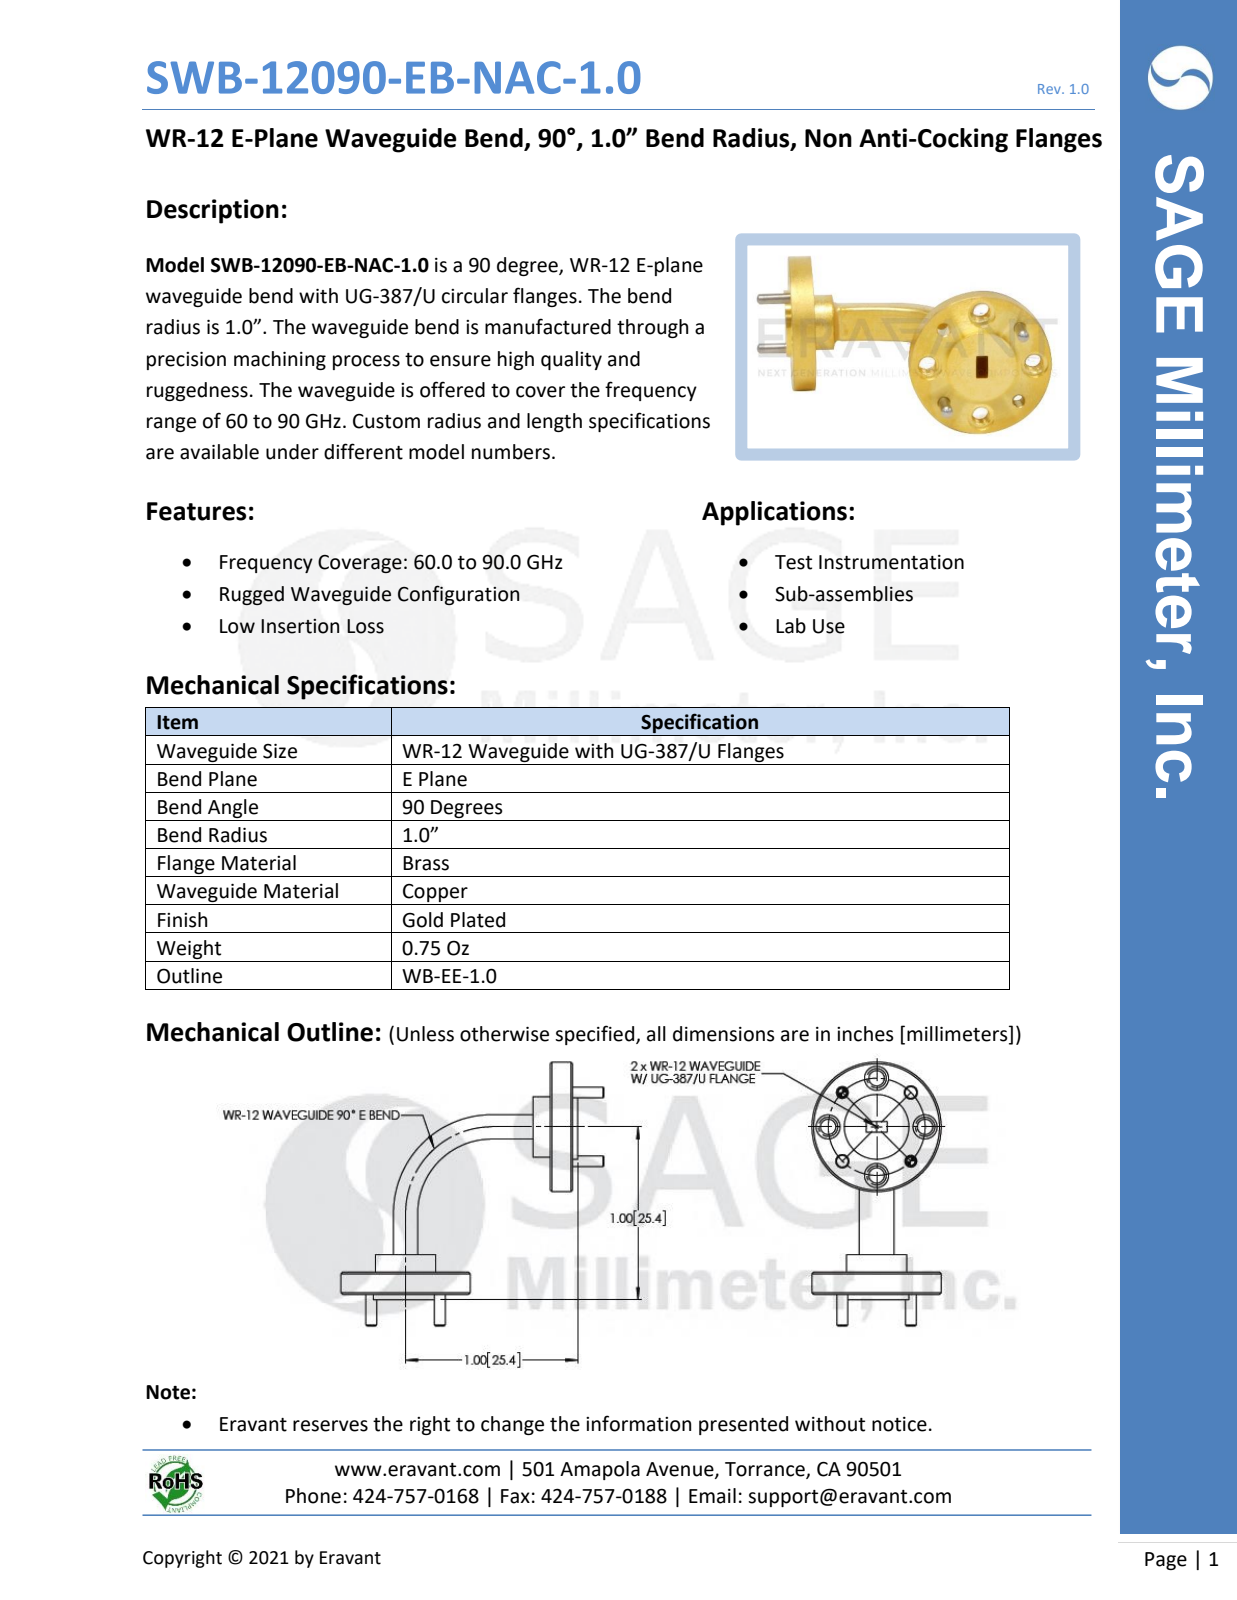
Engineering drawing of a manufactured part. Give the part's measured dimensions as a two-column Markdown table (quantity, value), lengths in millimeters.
| quantity | value |
| --- | --- |
| part name | SWB-12090-EB-1.0 |
| STEP written by | SolidWorks 2016 (AUTOMOTIVE_DESIGN) |
| units | millimeters |
| bodies | 5 solids, 146 faces (36 planar, 70 cylindrical, 40 other) |
| overall size | 38.8 × 38.8 × 19.1 |
| volume | 2 930 mm³ |
| surface area | 2 643 mm² |
| round holes (diameter × count) | 2.3 × 8, 3.6 × 8, 1.5 × 4, 1.7 × 4 |
| round bosses / shafts (diameter × count) | 1.6 × 4, 19.1 × 2, 9.5 × 2, 8.9 × 2 |
| partial cylindrical surfaces (radius × count) | 16.5 × 1, 21.6 × 1 |
| main face-to-face distances | 3.3, 5.1, 0.8, 4.1, 6.6, 5.8, 2.5, 1.3, 0.5, 2.8 |
| hole center spacings | 5.5, 10.1, 13.2, 14.3 |
